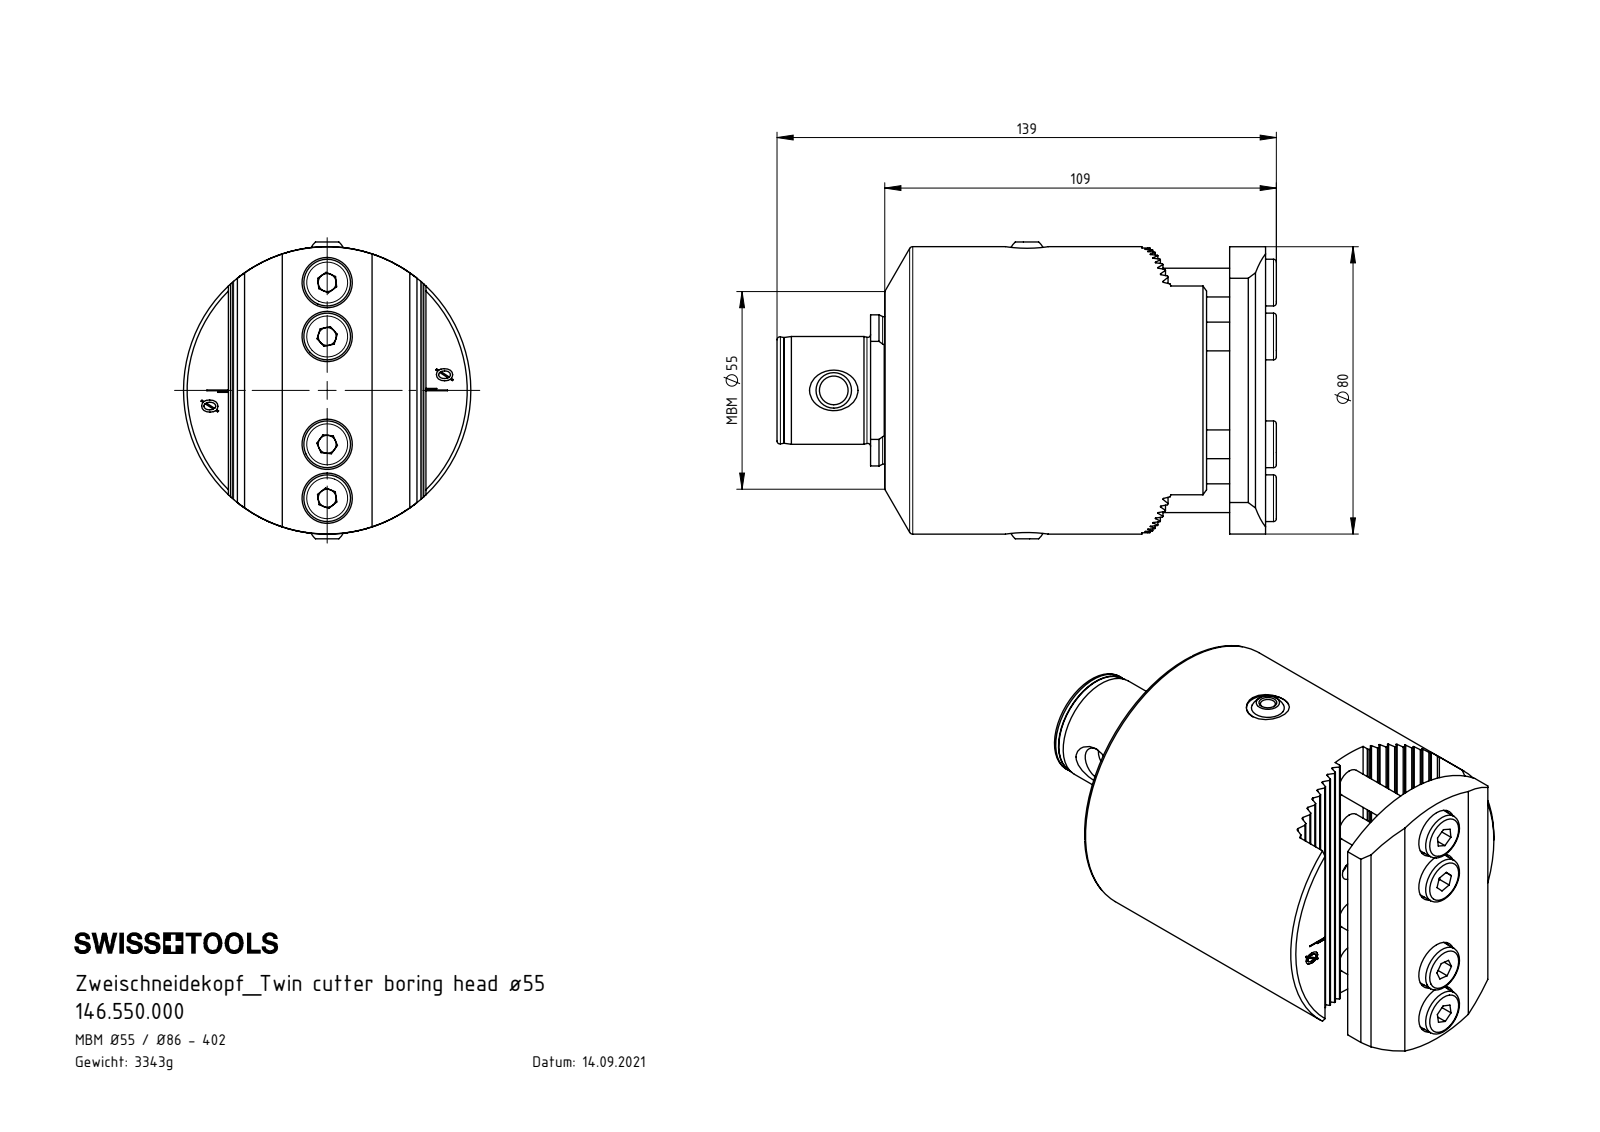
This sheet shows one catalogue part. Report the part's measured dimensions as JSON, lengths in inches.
{"part_name": "F00-WCB.136.001; 146.550.000; CCMT09T304; MB5-Z00.K21.112_C (+7 more)", "step_written_by": "SolidWorks 2017 (CONFIG_CONTROL_DESIGN)", "units": "inches", "bodies": {"solids": 16, "faces": 1533, "planar": 868, "cylindrical": 169, "other": 496}, "overall_size": [6.364, 5.592, 3.15], "volume_in3": 33.43, "surface_area_in2": 136.7, "round_holes": [[0.335, 5], [0.13, 4], [0.268, 4], [0.551, 4], [0.173, 2], [0.24, 2], [0.098, 1], [0.165, 1], [0.197, 1], [0.276, 1], [0.315, 1], [0.472, 1]], "round_bosses_or_shafts": [[0.512, 4], [0.315, 4], [0.207, 2], [0.157, 2], [3.15, 1], [1.181, 1]], "partial_cylinders_radius": [[0.008, 32], [0.013, 12], [0.023, 12], [1.575, 8], [0.031, 2], [0.828, 1]], "face_to_face_distances": [0.094, 0.187, 0.281, 0.839, 1.327, 0.375, 0.488, 0.375, 0.563, 0.281], "hole_center_spacings": [0.591, 1.181, 0.239, 0.244, 1.772, 5.394, 5.62, 5.625]}
